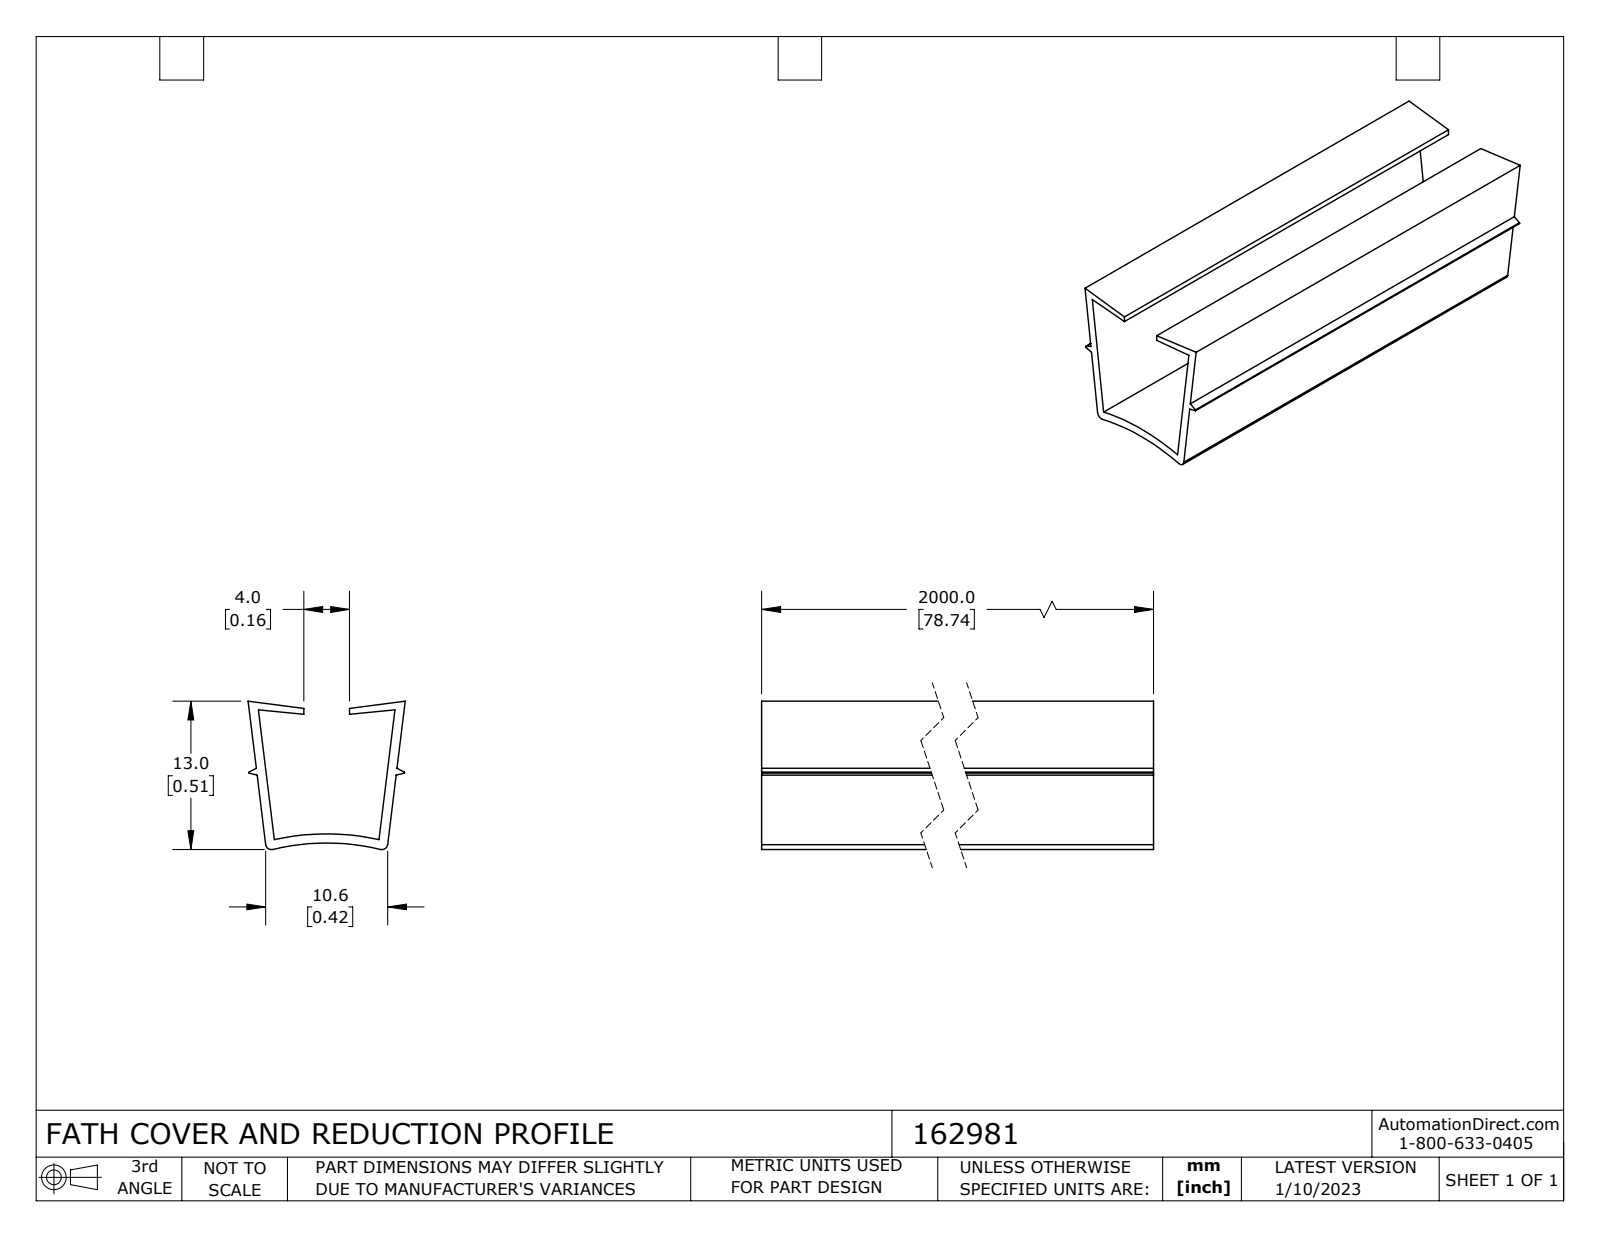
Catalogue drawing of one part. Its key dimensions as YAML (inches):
part_name: "162981"
step_written_by: "SolidWorks 2021 (CONFIG_CONTROL_DESIGN)"
units: inches
bodies: {solids: 1, faces: 25, planar: 18, cylindrical: 7, other: 0}
overall_size: [1.575, 0.54, 0.51]
volume: 0.081
surface_area: 5.628
partial_cylinders:
  - {radius: 0.02, count: 2}
  - {radius: 0.787, count: 1}
  - {radius: 0.819, count: 1}
face_to_face_distances: [0.031, 1.575, 0.157]
